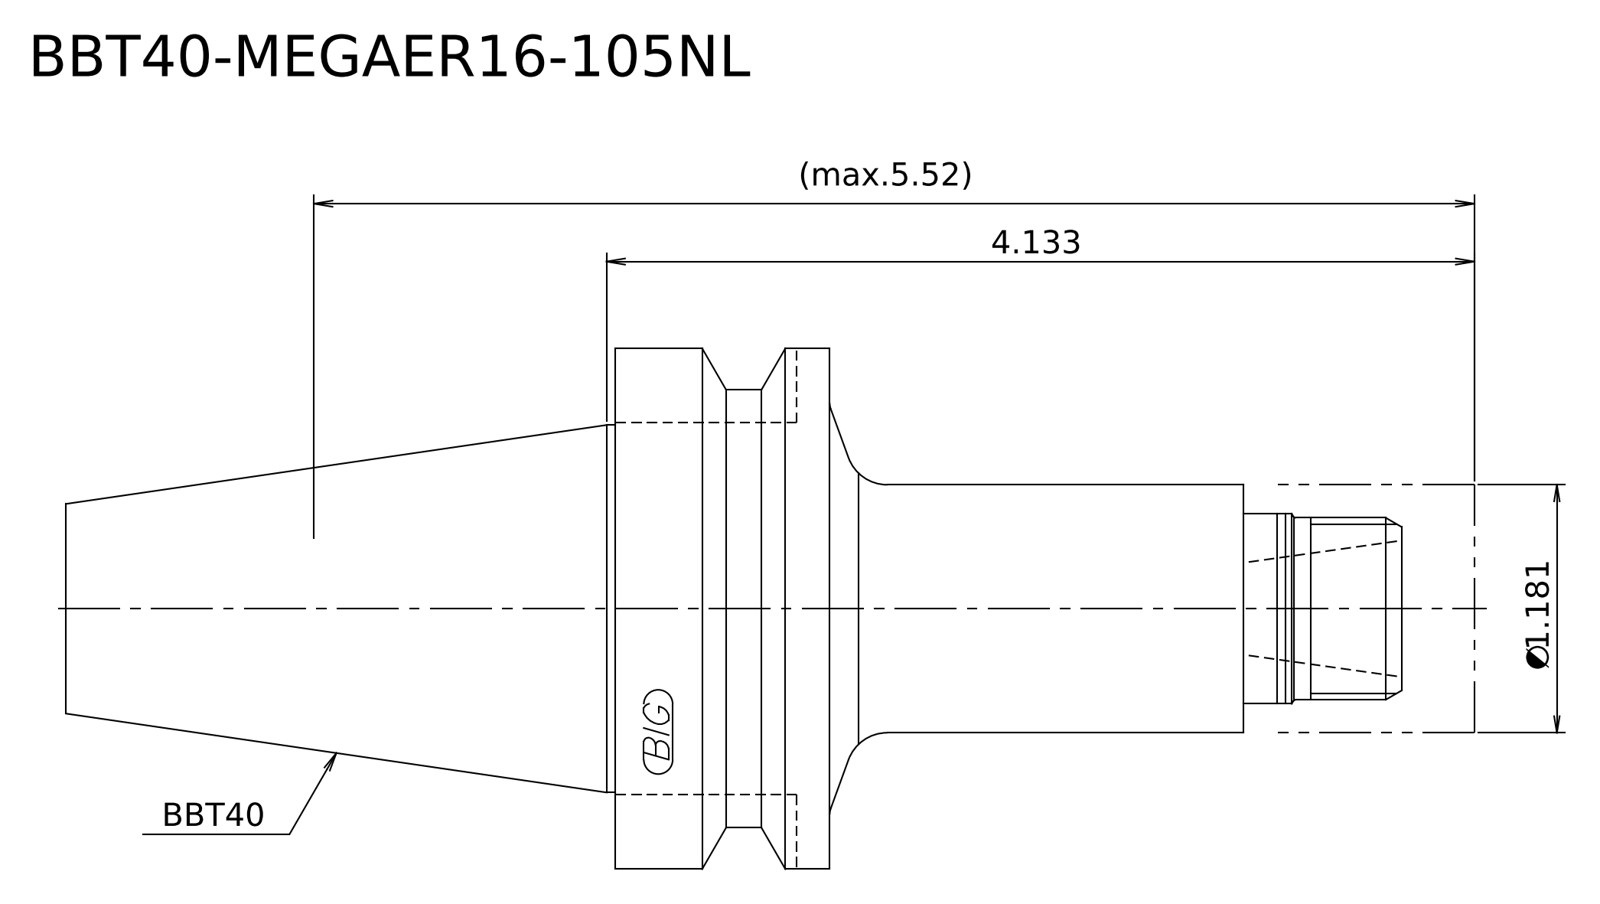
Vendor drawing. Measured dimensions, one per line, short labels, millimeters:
written by: Kubotek KeyCreator 2011 V10.0.2 (22737) (automotive_design)
unit: mm
bodies: 2 solids, 21 faces (7 planar, 8 cylindrical, 6 other)
size: 170.4 × 63 × 63
volume: 204 582 mm³; area: 27 926 mm²
bosses: 1× ⌀63, 1× ⌀53, 1× ⌀44.45, 1× ⌀30, 1× ⌀23, 1× ⌀22
face distances: 26, 53, 79, 25, 78, 104, 170.4, 145.4, 92.4, 66.4
